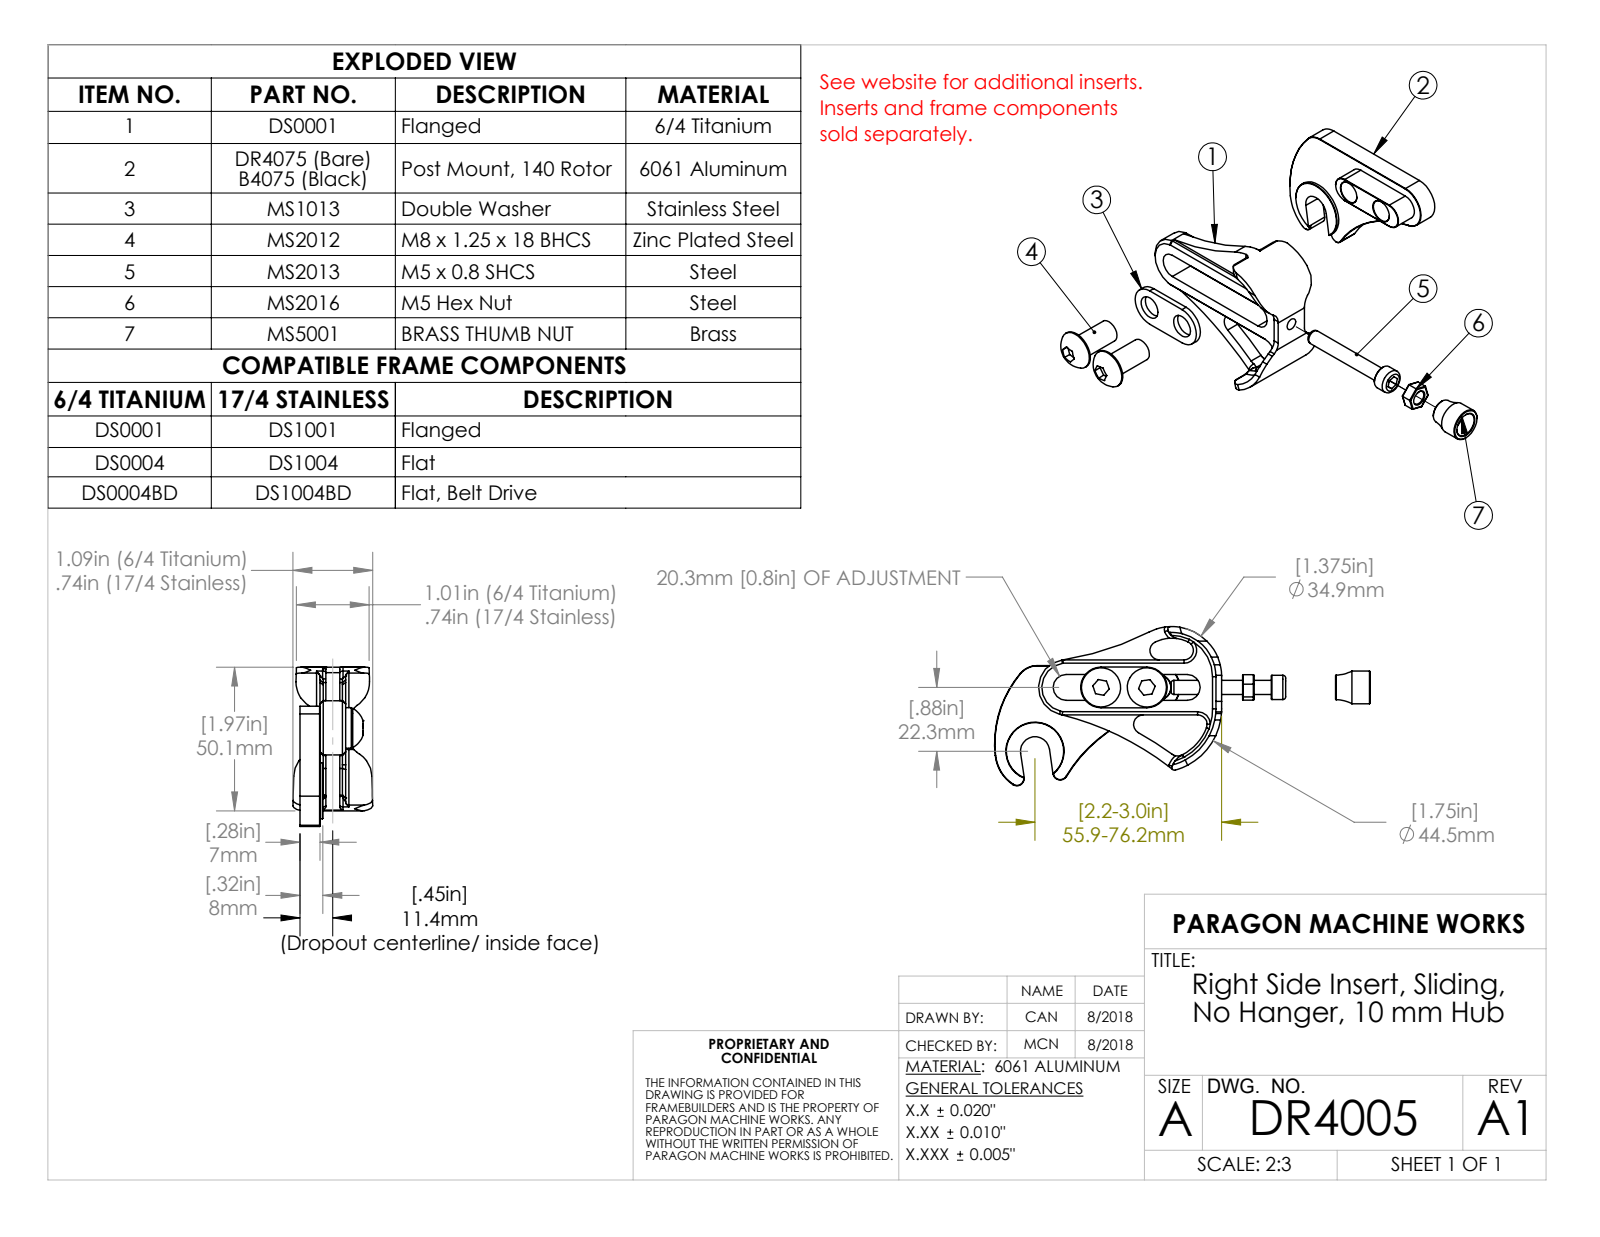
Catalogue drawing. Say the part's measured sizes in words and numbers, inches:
The part is named "DR4005". Its 3-D file was written by "SolidWorks 2023 (AUTOMOTIVE_DESIGN)". It is 1 solid with 47 faces: 12 planar, 18 cylindrical and 17 other. Overall it measures 2.358 by 2.053 by 0.59 inches. Its volume is 0.733 cubic inches and its surface area 8.999 square inches. Round holes: 2 of diameter 0.312. Round bosses or shafts: 1 of diameter 0.8. Partial cylindrical surfaces (rounded edges, fillets, slot ends): 2 of radius 0.1, 2 of radius 0.178, 2 of radius 0.3, 1 of radius 0.2, 1 of radius 0.55, 1 of radius 1.5, 1 of radius 2. The main face-to-face distances are 0.275, 0.315, 0.04, 0.478, 0.356, 0.122, 0.59, 0.4, 0.136. The hole center spacings are 0.63.
